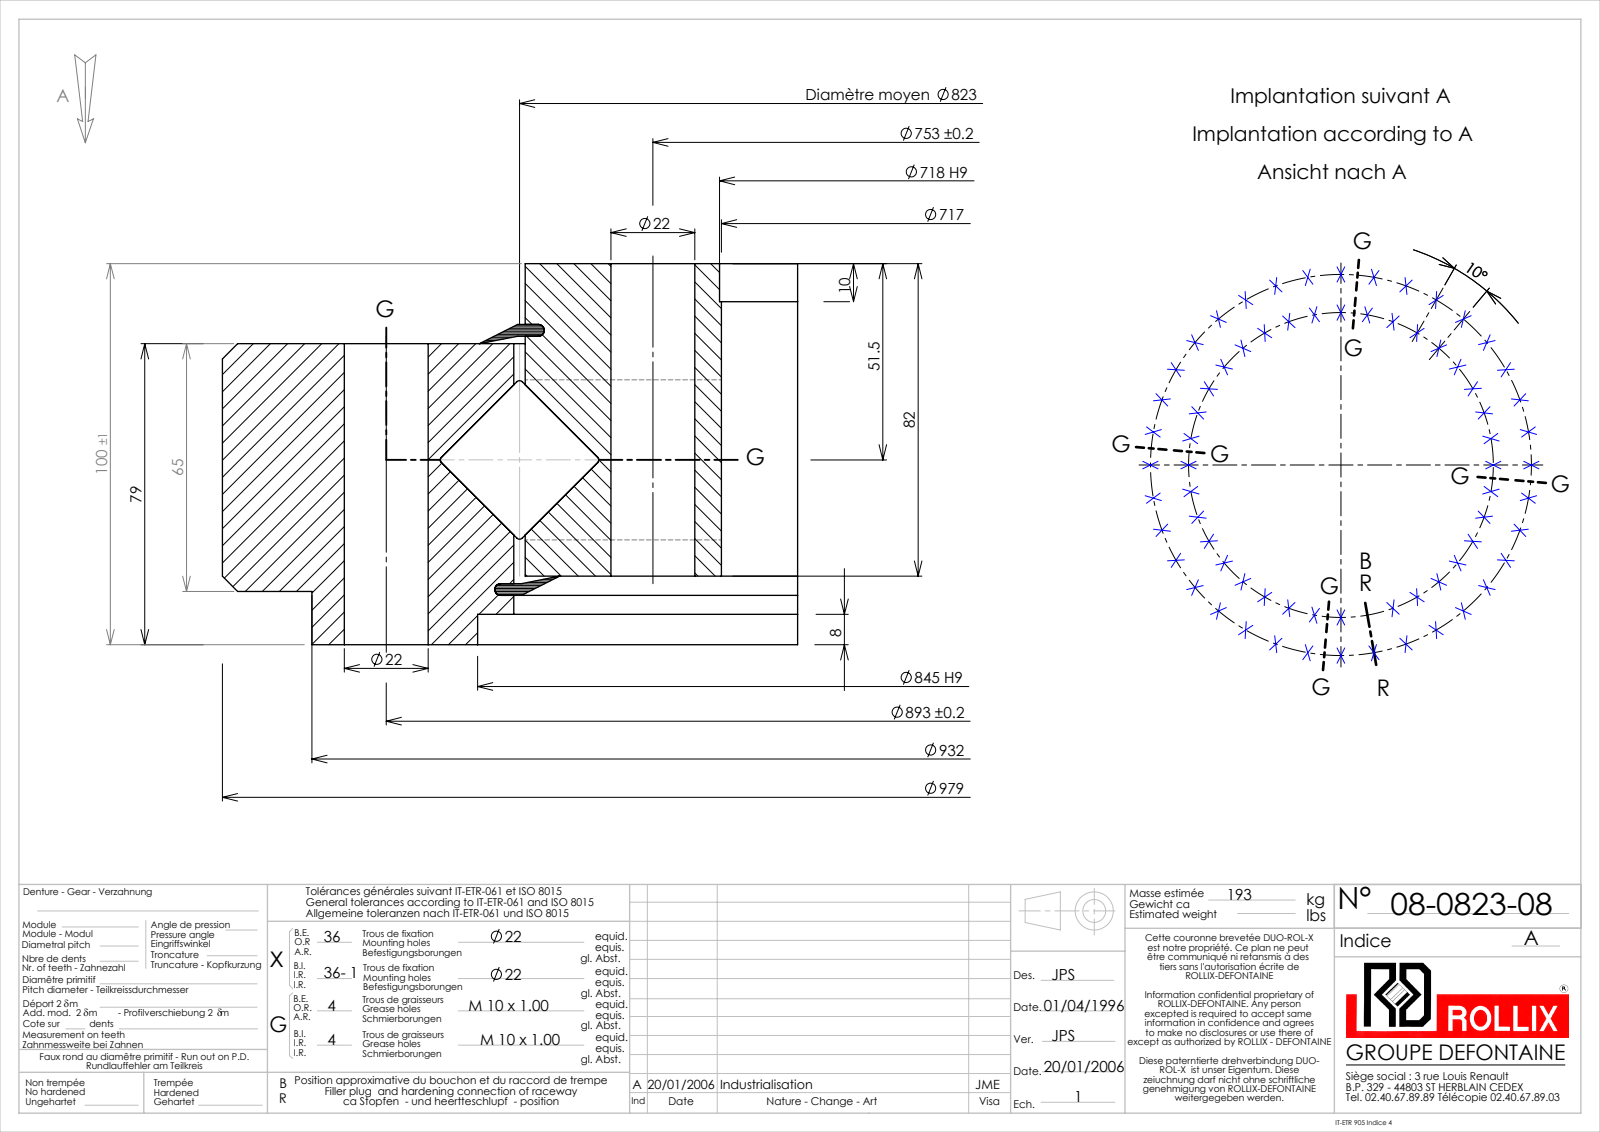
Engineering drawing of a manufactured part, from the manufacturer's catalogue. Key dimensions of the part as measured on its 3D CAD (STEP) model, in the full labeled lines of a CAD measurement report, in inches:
Part name (STEP PRODUCT): 08-0823-08
STEP written by: SolidWorks 2016 (CONFIG_CONTROL_DESIGN)
Units: inches
Bodies: 5 solids, 247 faces (17 planar, 178 cylindrical, 52 other)
Overall size (bounding box): 38.543 × 38.543 × 3.937
Volume: 1 344 in³ · Surface area: 3 377 in²
Round holes (diameter × count): ⌀0.866 ×71, ⌀0.354 ×6, ⌀28.228 ×1, ⌀28.268 ×1, ⌀32.52 ×1, ⌀33.268 ×1
Round bosses / shafts (diameter × count): ⌀38.543 ×1, ⌀36.693 ×1, ⌀32.283 ×1, ⌀1.181 ×1
Main face-to-face distances: 2.402, 3.228, 0.827, 0.709, 3.11, 3.937, 0.551, 0.157, 2.559, 3.386
Hole centre spacings: 3.064, 30.447, 33.959, 35.024, 12.024, 20.165, 14.858, 22.599
